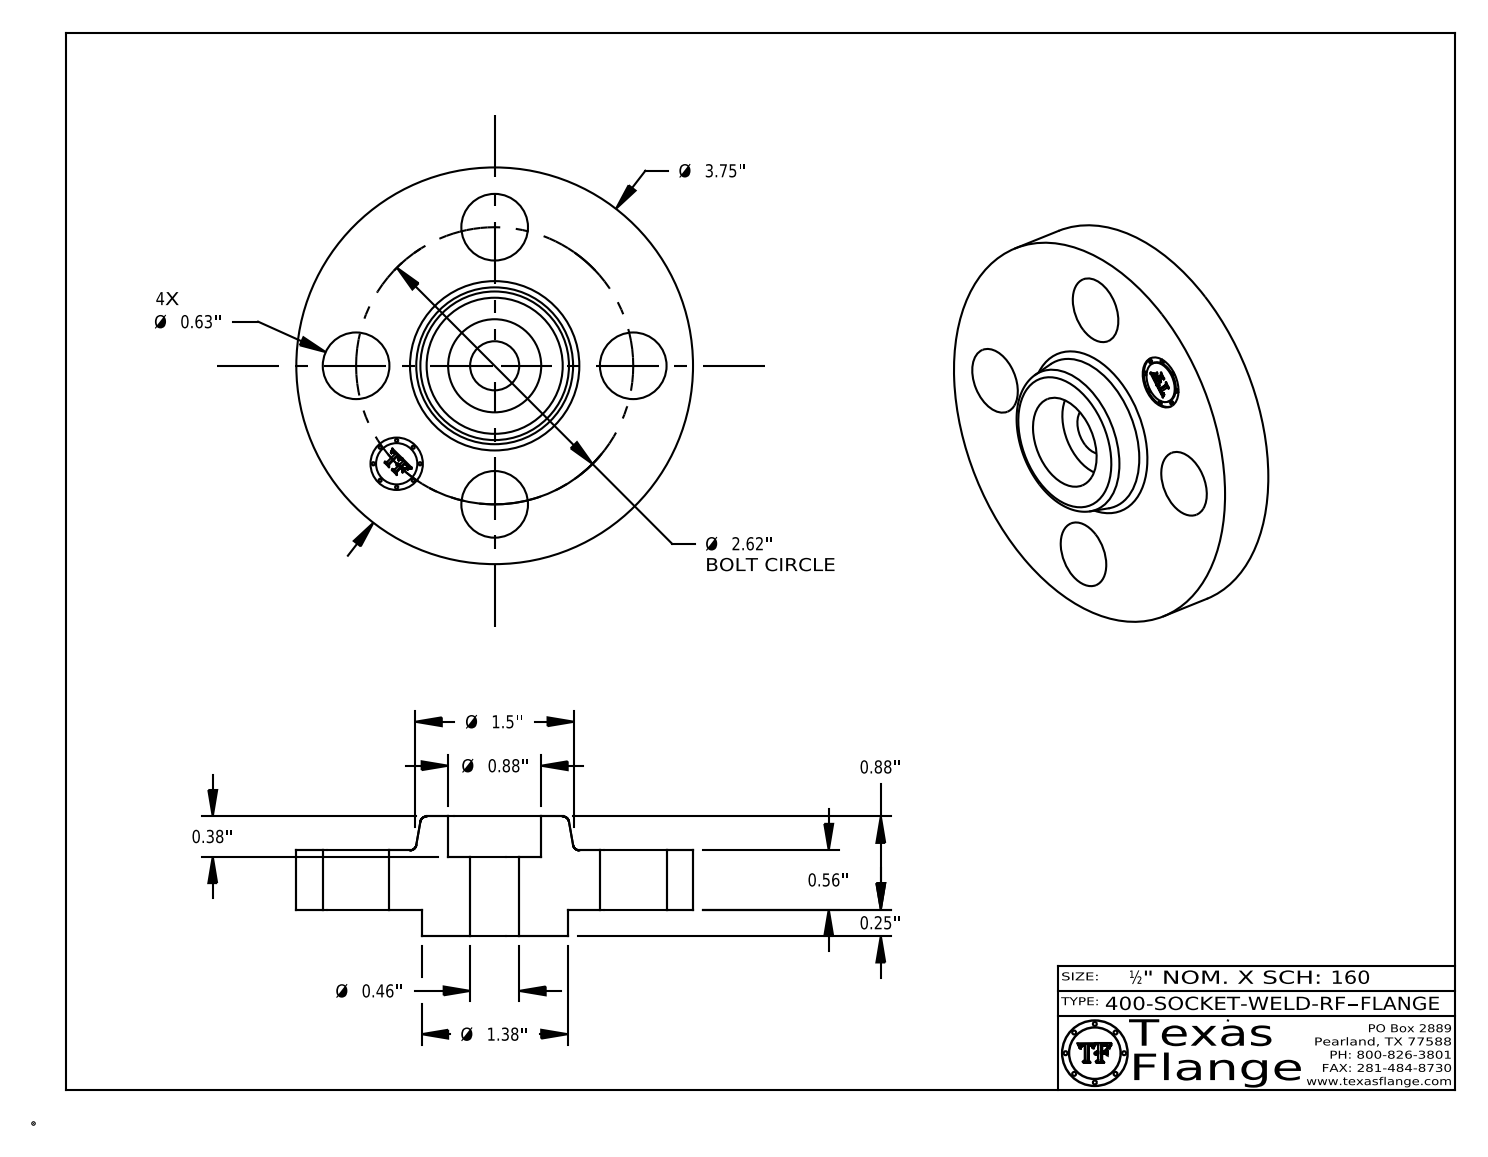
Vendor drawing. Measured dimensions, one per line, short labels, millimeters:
name: 400-SOCKET-WELD-RF
written by: CATIA V5 STEP AP214 (AUTOMOTIVE_DESIGN)
unit: mm
bodies: 1 solid, 412 faces (370 planar, 36 cylindrical, 6 other)
size: 95.3 × 95.3 × 28.7
volume: 98 750 mm³; area: 22 370 mm²
holes: 4× ⌀16, 1× ⌀11.8, 1× ⌀12.6, 1× ⌀22.4
bosses: 8× ⌀0.8, 1× ⌀95.3, 1× ⌀35.1, 1× ⌀9.9
face distances: 14.2, 6.4, 20.6, 28.7, 22.4, 8.1, 19.1, 12.7, 1.5, 9.7
hole spacings: 33.3, 47, 25.5, 61.5, 66.5, 33.3
